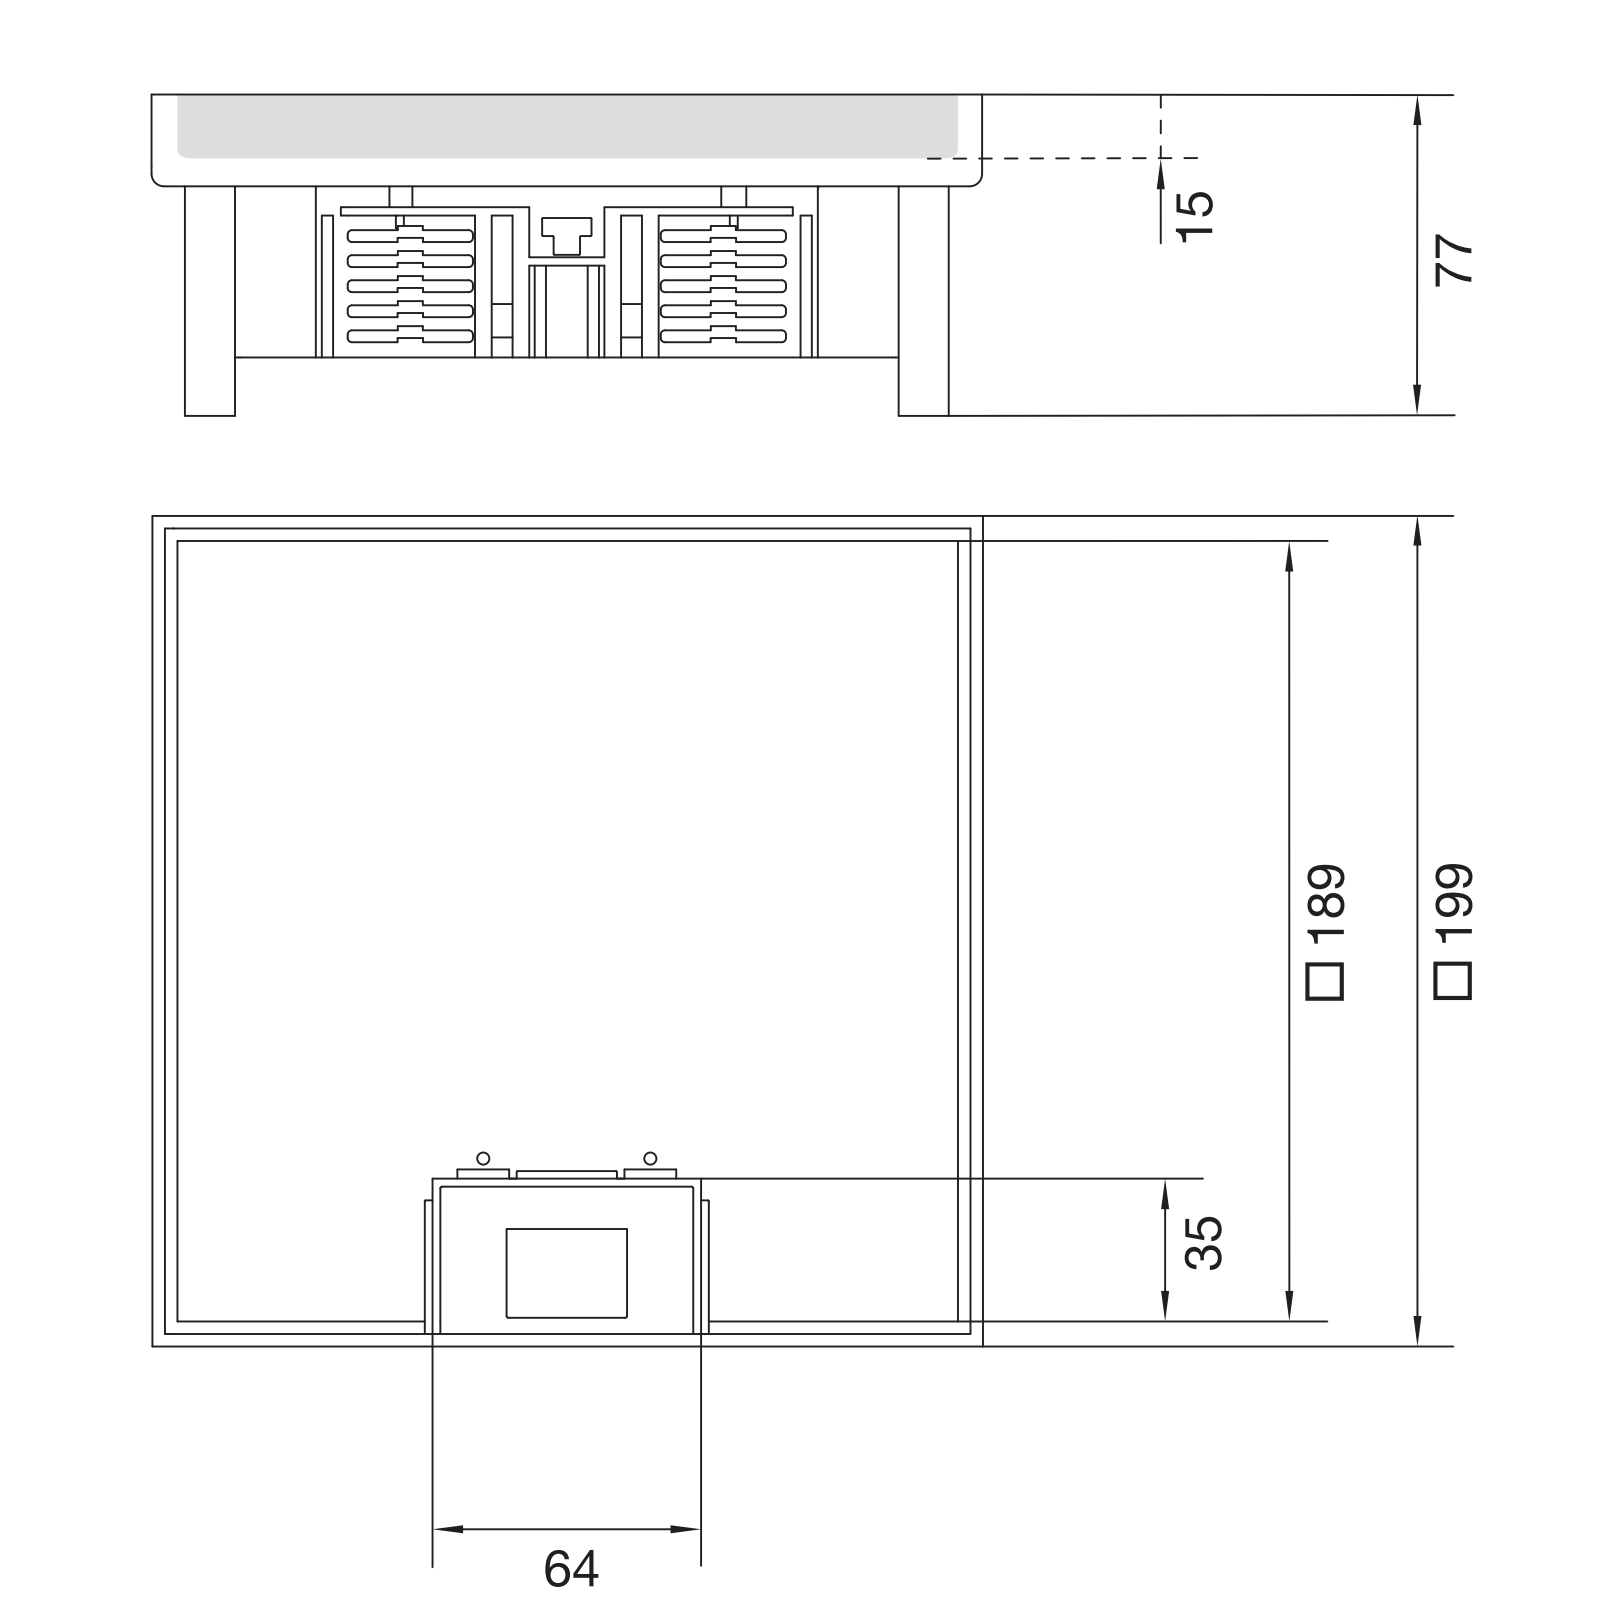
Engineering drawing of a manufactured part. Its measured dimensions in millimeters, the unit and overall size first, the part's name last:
Units: millimetres
Overall size (bounding box): 199 × 199 × 87
Round holes (diameter × count): ⌀6.8 ×4, ⌀8.5 ×4, ⌀2.7 ×2
Round bosses / shafts (diameter × count): ⌀12 ×4, ⌀9.85 ×4
Partial cylindrical surfaces — rounded edges, fillets, slot ends (radius × count): R1 ×8, R3 ×8, R105 ×5, R6.6 ×1, R107 ×1
Main face-to-face distances: 2, 15, 197, 2.5, 3, 194, 17, 174.5, 153.5, 24
Hole centre spacings: 171, 72.47, 109.96, 154.56, 175.3, 241.83, 40
Volume: 251 407 mm³ · Surface area: 250 768 mm²
Bodies: 10 solids, 306 faces (229 planar, 67 cylindrical, 10 other)
Part name (STEP PRODUCT): T-00596GEN_1_1; T-00595_1_1_2; T-00805_ASM_1_1_ASM; U09001_1_1_2 (+8 more)
STEP written by: CREO PARAMETRIC BY PTC INC, 2022281 (AUTOMOTIVE_DESIGN)
